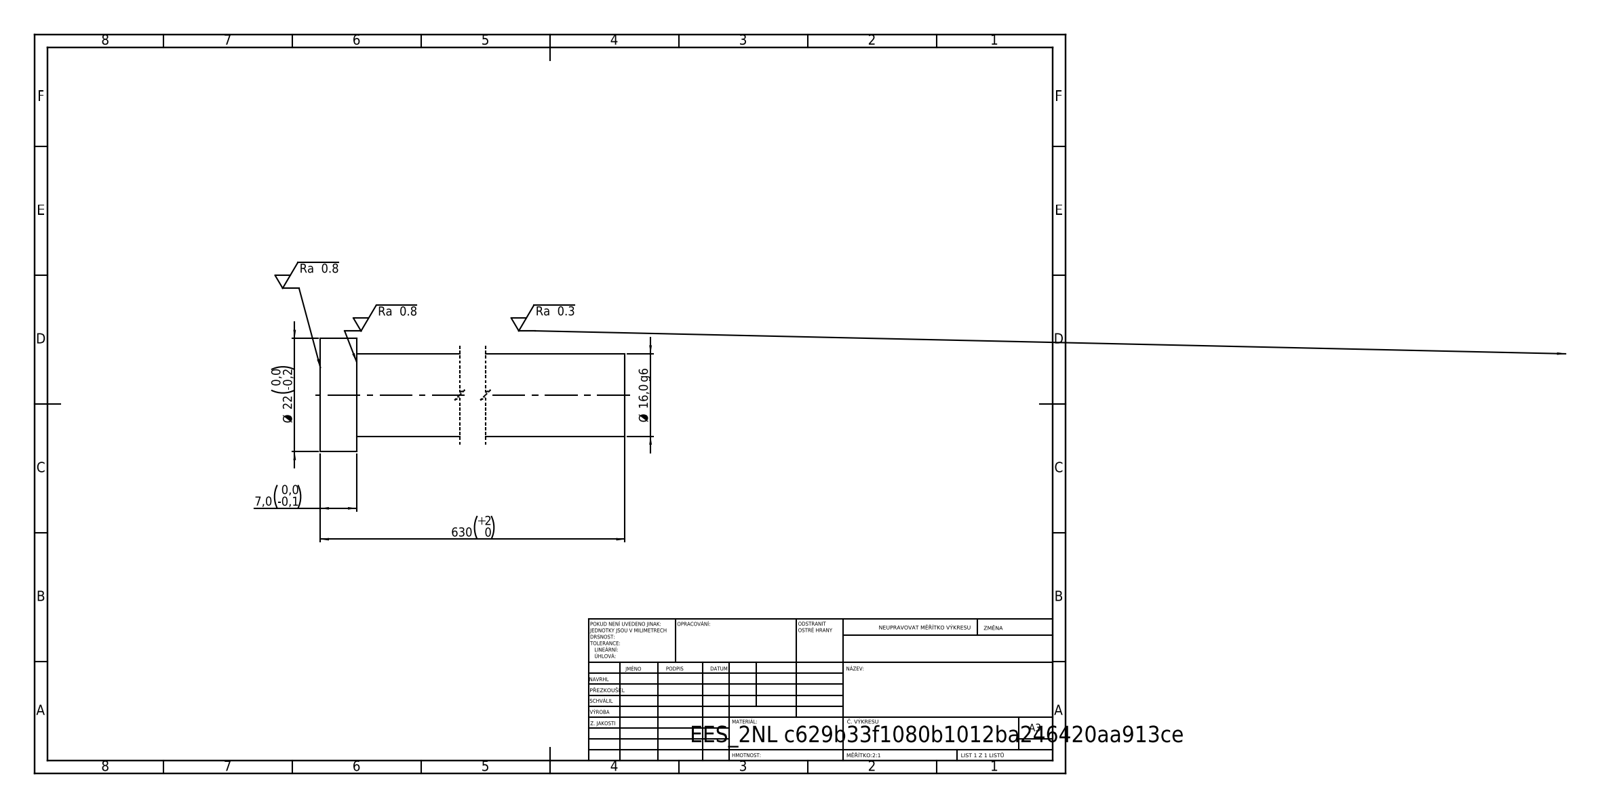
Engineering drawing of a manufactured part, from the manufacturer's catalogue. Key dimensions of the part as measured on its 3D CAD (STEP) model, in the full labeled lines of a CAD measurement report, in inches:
STEP written by: SolidWorks 2019 (CONFIG_CONTROL_DESIGN)
Units: inches
Bodies: 1 solid, 7 faces (3 planar, 4 cylindrical, 0 other)
Overall size (bounding box): 24.803 × 0.866 × 0.866
Volume: 7.806 in³ · Surface area: 50.47 in²
Round bosses / shafts (diameter × count): ⌀0.866 ×1, ⌀0.63 ×1
Main face-to-face distances: 24.803, 0.276, 24.528
